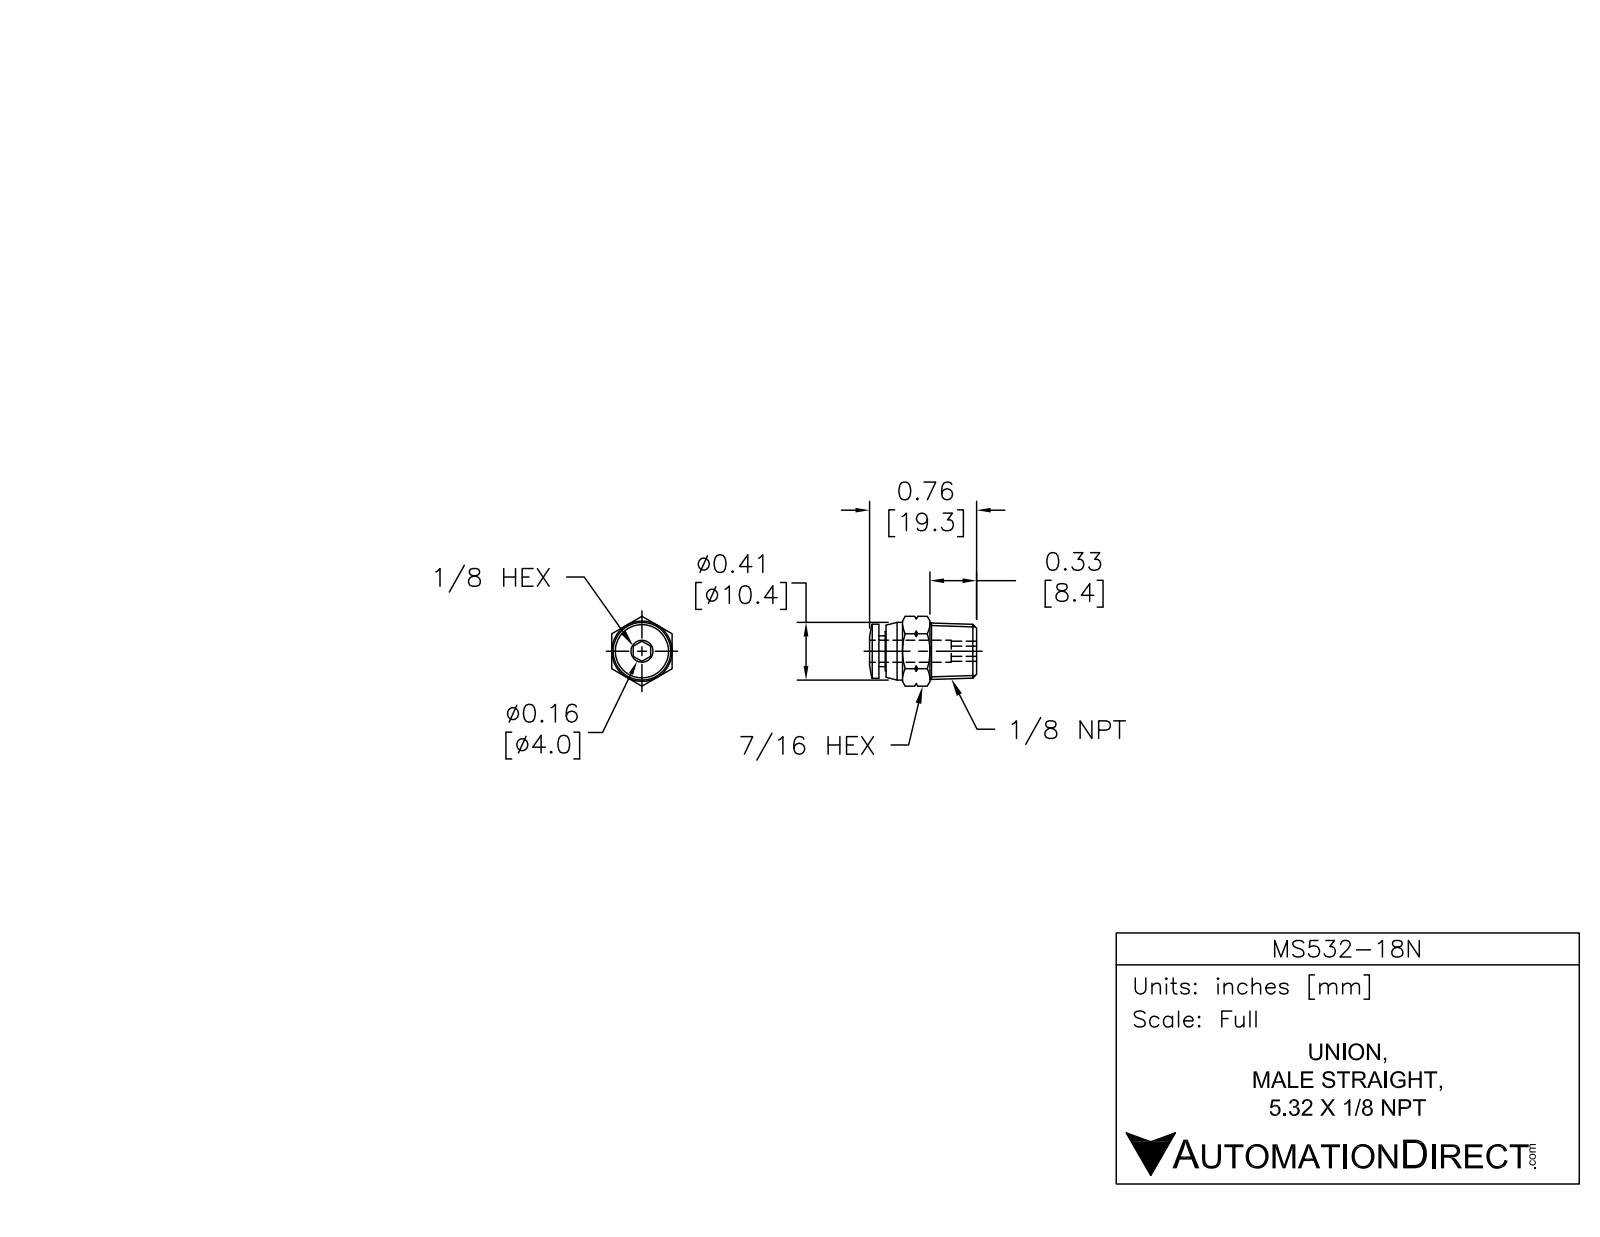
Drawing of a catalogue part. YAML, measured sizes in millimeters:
part_name: "PC5-32--N01"
step_written_by: "Autodesk Inventor 2008 (AUTOMOTIVE_DESIGN)"
units: millimeters
bodies: {solids: 1, faces: 50, planar: 13, cylindrical: 6, other: 31}
overall_size: [19.5, 12.7, 11]
volume: 1330
surface_area: 1115
round_holes:
  - {diameter: 3.2, count: 1}
  - {diameter: 4.3, count: 1}
round_bosses_or_shafts:
  - {diameter: 10.5, count: 1}
  - {diameter: 9.85, count: 1}
  - {diameter: 7.2, count: 1}
  - {diameter: 5.6, count: 1}
face_to_face_distances: [11, 17.8, 16.5, 1.3, 16.65, 1.15, 8.5, 8, 8.15, 9.3]
